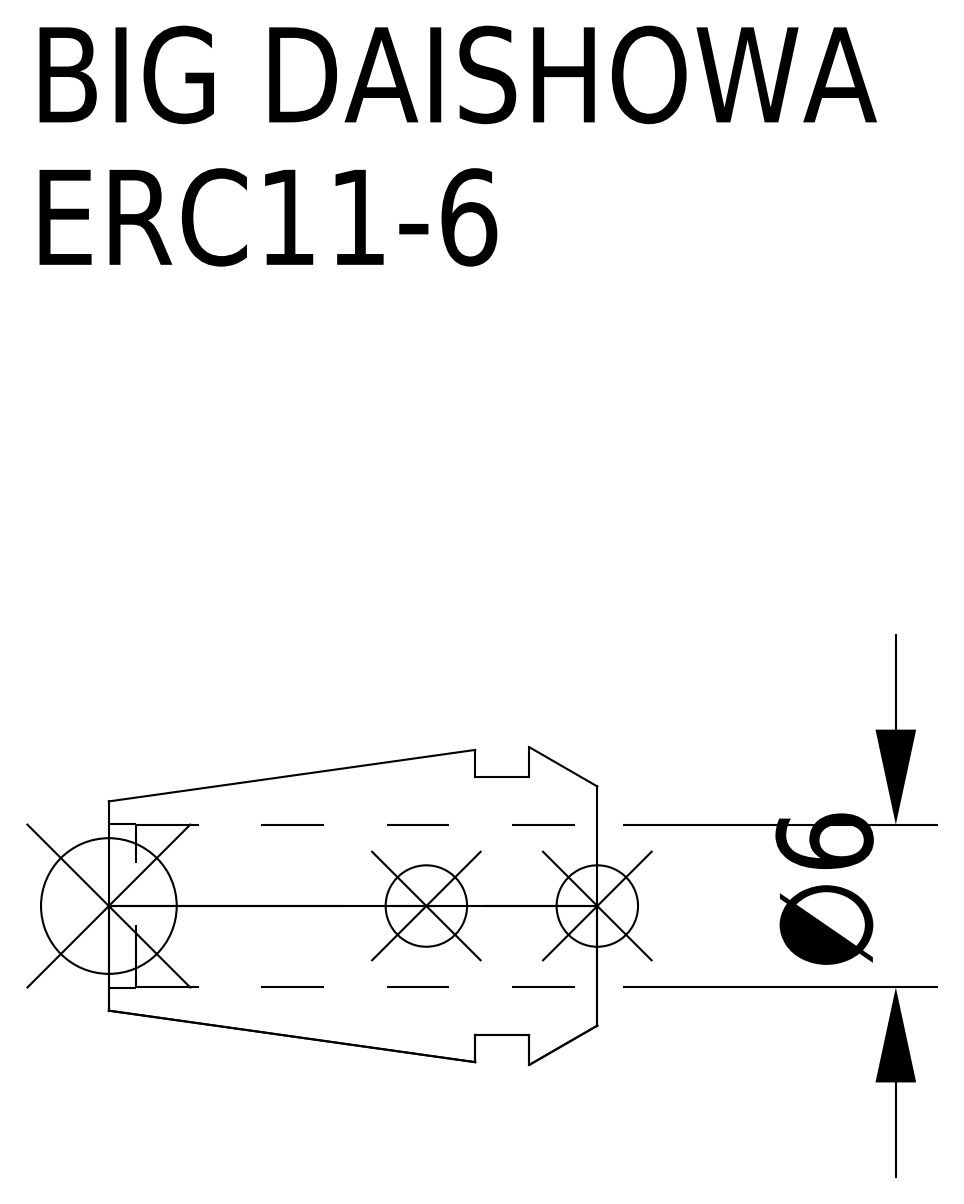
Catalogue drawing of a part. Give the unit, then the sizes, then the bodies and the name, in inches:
Units: inches
Overall size (bounding box): 0.709 × 0.461 × 0.461
Round holes (diameter × count): ⌀0.236 ×1, ⌀0.238 ×1
Round bosses / shafts (diameter × count): ⌀0.374 ×1
Main face-to-face distances: 0.079, 0.098, 0.177, 0.709, 0.61, 0.531, 0.669, 0.571, 0.492, 0.039
Volume: 0.051 in³ · Surface area: 1.589 in²
Bodies: 1 solid, 15 faces (5 planar, 6 cylindrical, 4 other)
Part name (STEP PRODUCT): ERC11-6
STEP written by: CREO PARAMETRIC BY PTC INC, 2016380 (AUTOMOTIVE_DESIGN)
